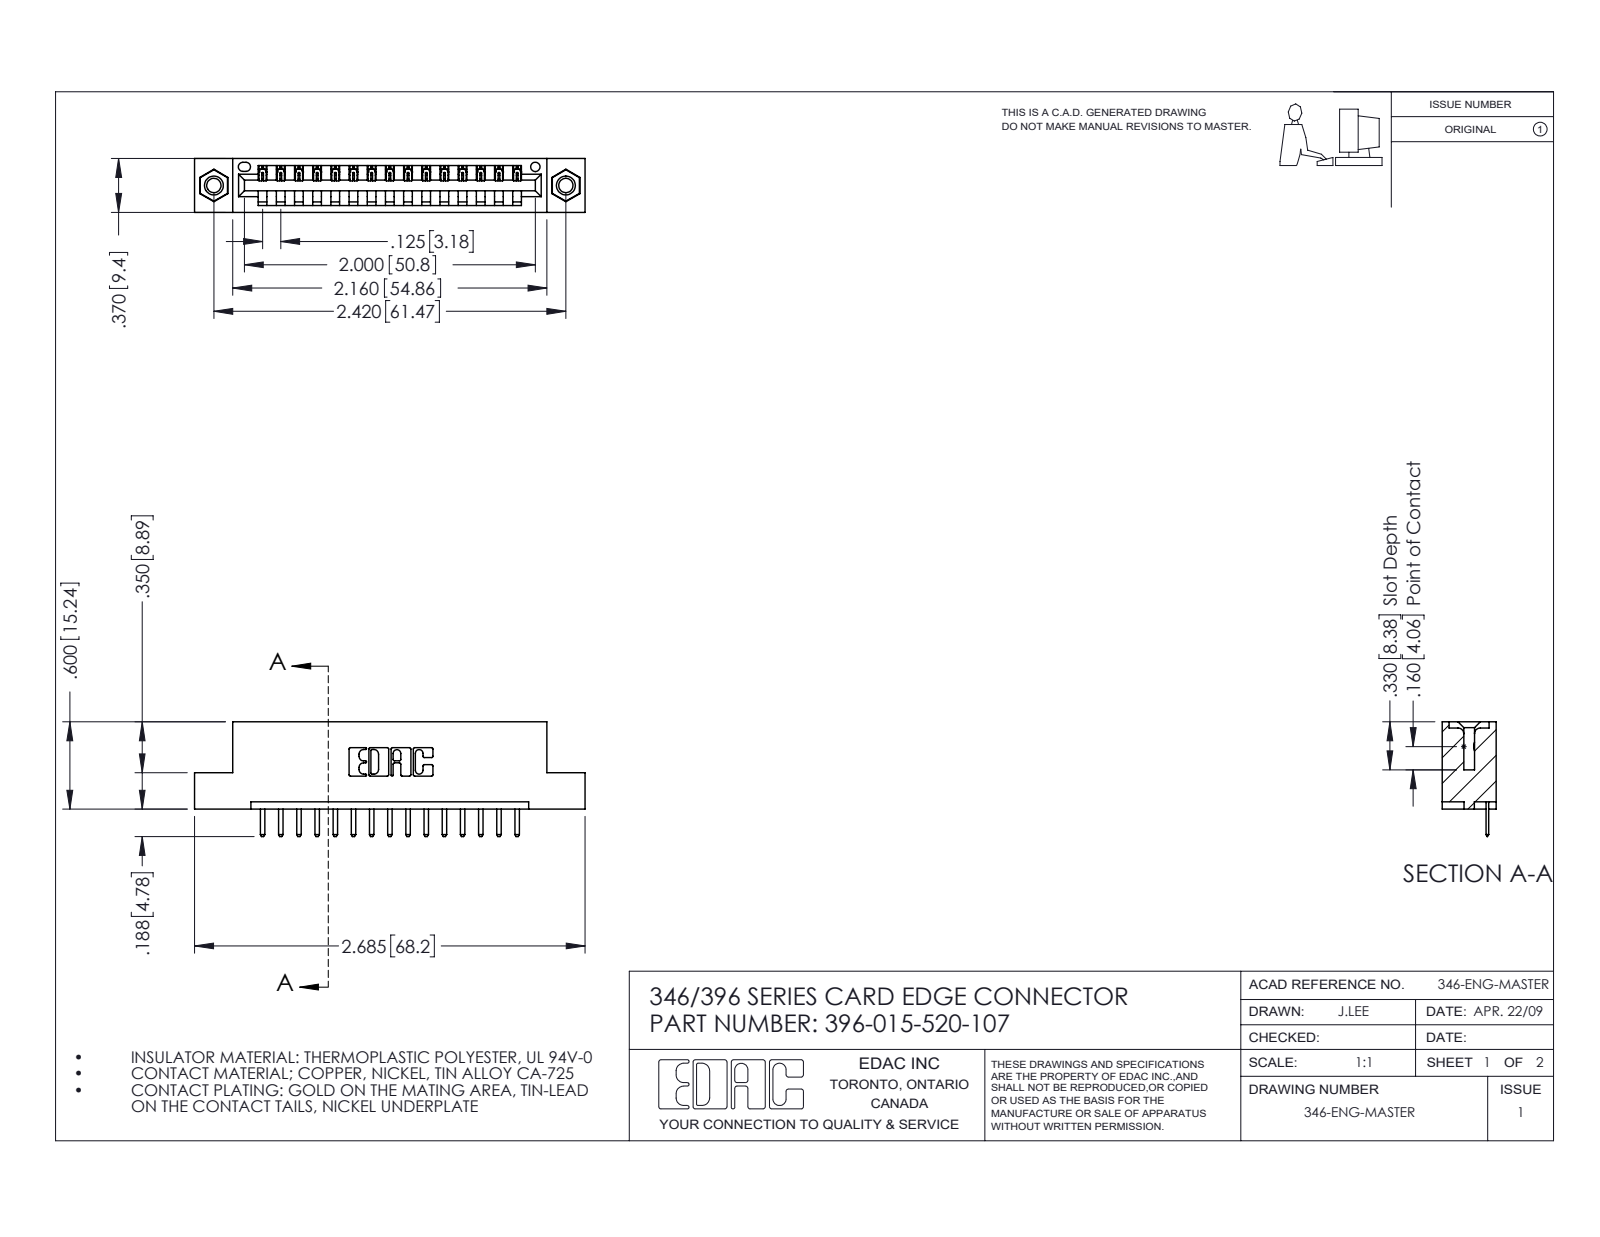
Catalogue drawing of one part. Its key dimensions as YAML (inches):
part_name: "345-292-001_345-293-120; 345-250-001_345-250-005-103; 396-015-520-107; 346 Part_Flush Mounting Lugs - 0.156 Dia-TI"
step_written_by: "SolidWorks 2016 (CONFIG_CONTROL_DESIGN)"
units: inches
bodies: {solids: 18, faces: 1112, planar: 738, cylindrical: 358, other: 16}
overall_size: [2.685, 0.788, 0.37]
volume: 0.384
surface_area: 11.56
round_holes:
  - {diameter: 0.098, count: 2}
  - {diameter: 0.125, count: 2}
  - {diameter: 0.156, count: 2}
  - {diameter: 0.064, count: 1}
round_bosses_or_shafts:
  - {diameter: 0.155, count: 2}
partial_cylinders:
  - {radius: 0.01, count: 32}
  - {radius: 0.006, count: 30}
  - {radius: 0.01, count: 22}
  - {radius: 0.007, count: 6}
  - {radius: 0.031, count: 6}
  - {radius: 0.026, count: 3}
  - {radius: 0.031, count: 2}
  - {radius: 0.04, count: 2}
face_to_face_distances: [0.37, 0.25, 0.048, 0.322, 0.148, 0.222, 0.1, 0.174, 0.072, 0.298]
hole_center_spacings: [0.246, 2.213, 2.42]
